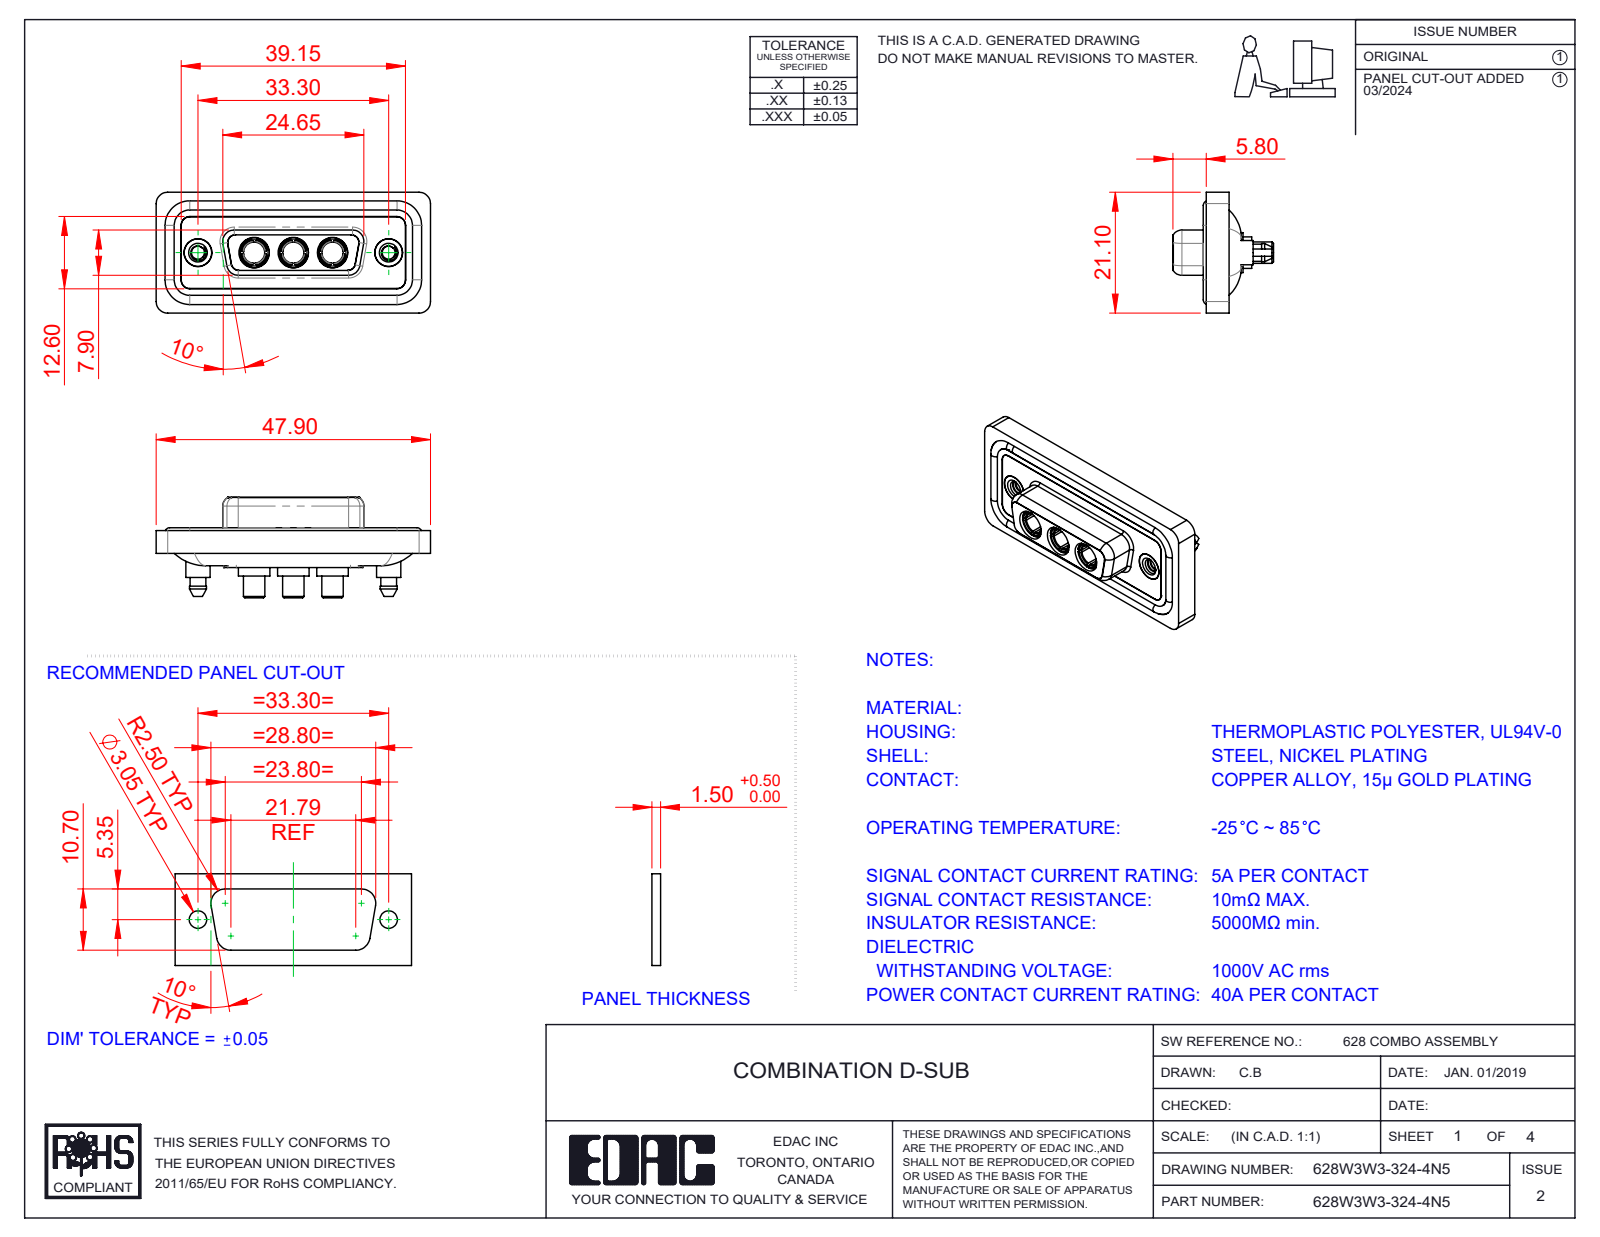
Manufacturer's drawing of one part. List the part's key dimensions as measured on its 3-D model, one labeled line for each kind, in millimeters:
Part name (STEP PRODUCT): 628Combo Waterproof Housing_15 Contacts; 628Combo Shell Front_15 Contacts; Power Socket_40A S; 628Combo Housing_3W3 (+3 more)
STEP written by: SolidWorks 2023 (CONFIG_CONTROL_DESIGN)
Units: millimetres
Bodies: 13 solids, 658 faces (208 planar, 289 cylindrical, 161 other)
Overall size (bounding box): 47.9 × 21.1 × 17.55
Volume: 6 215 mm³ · Surface area: 10 104 mm²
Round holes (diameter × count): ⌀4.85 ×5, ⌀3.7 ×3, ⌀5.3 ×3, ⌀2.26 ×2, ⌀4 ×2, ⌀4.05 ×2, ⌀5 ×2
Round bosses / shafts (diameter × count): ⌀1.6 ×4, ⌀5.5 ×3, ⌀5.2 ×3, ⌀4.96 ×3, ⌀4.75 ×3, ⌀3.75 ×3, ⌀5.4 ×2, ⌀4.95 ×2
Partial cylindrical surfaces — rounded edges, fillets, slot ends (radius × count): R1.5 ×24, R2 ×20, R1.35 ×12, R1.6 ×10, R0.25 ×4, R0.5 ×4, R0.6 ×4, R0.65 ×4
Main face-to-face distances: 0.4, 1.8, 1.6, 0.5, 7.45, 1.1, 2.9, 5.65, 7.05, 6.6
Hole centre spacings: 6.85, 9.8, 16.65, 23.5, 13.7, 33.3
